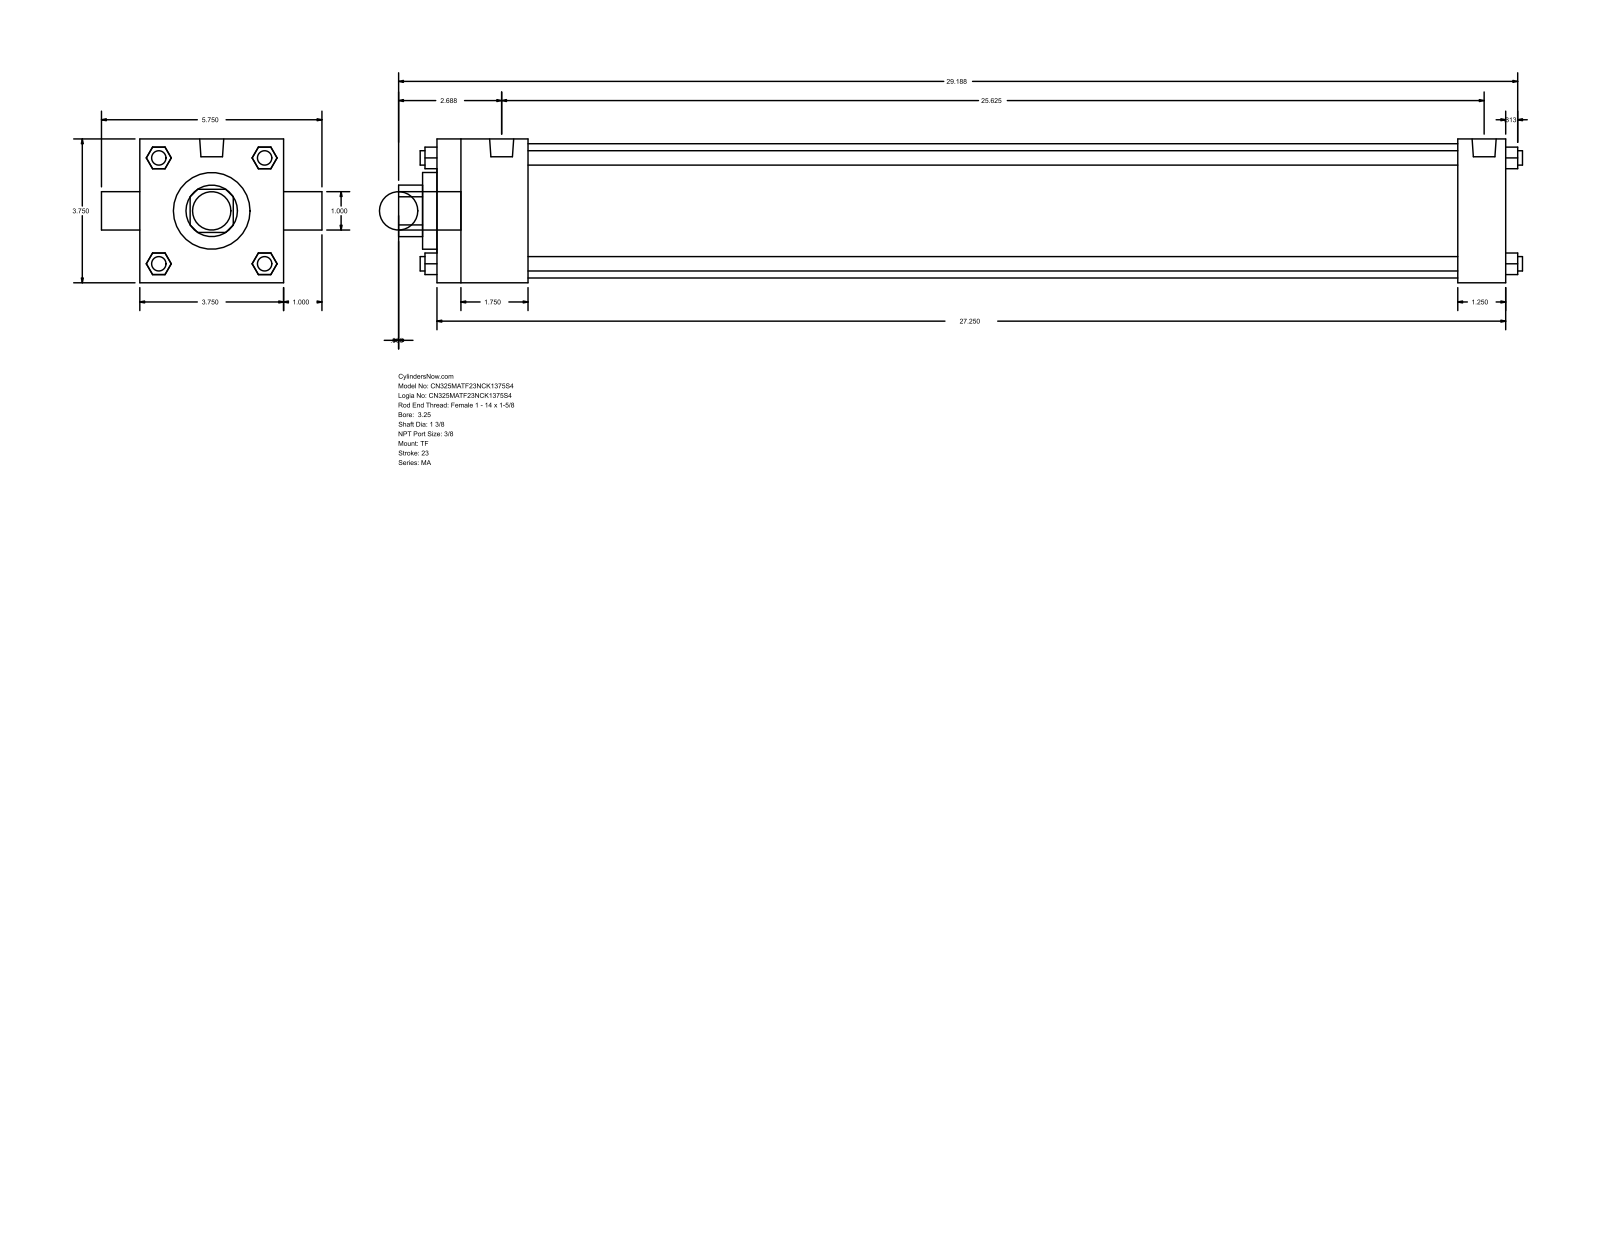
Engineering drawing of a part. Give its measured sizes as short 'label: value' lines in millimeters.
name: MA_TF__0325_1.375
written by: GSSL Pune (CONFIG_CONTROL_DESIGN)
unit: mm
bodies: 0 solids, 120 faces (92 planar, 28 cylindrical, 0 other)
size: 744.54 × 146.05 × 95.25
holes: 1× ⌀25.4, 1× ⌀34.92, 1× ⌀50.8, 1× ⌀88.9
bosses: 4× ⌀9.53, 3× ⌀11.11, 2× ⌀15.93, 1× ⌀25.4
rounds: 1× R17.06
face distances: 95.24, 708.02, 60.32, 676.27, 615.95, 647.7, 31.75, 9.52, 69.84, 685.79
